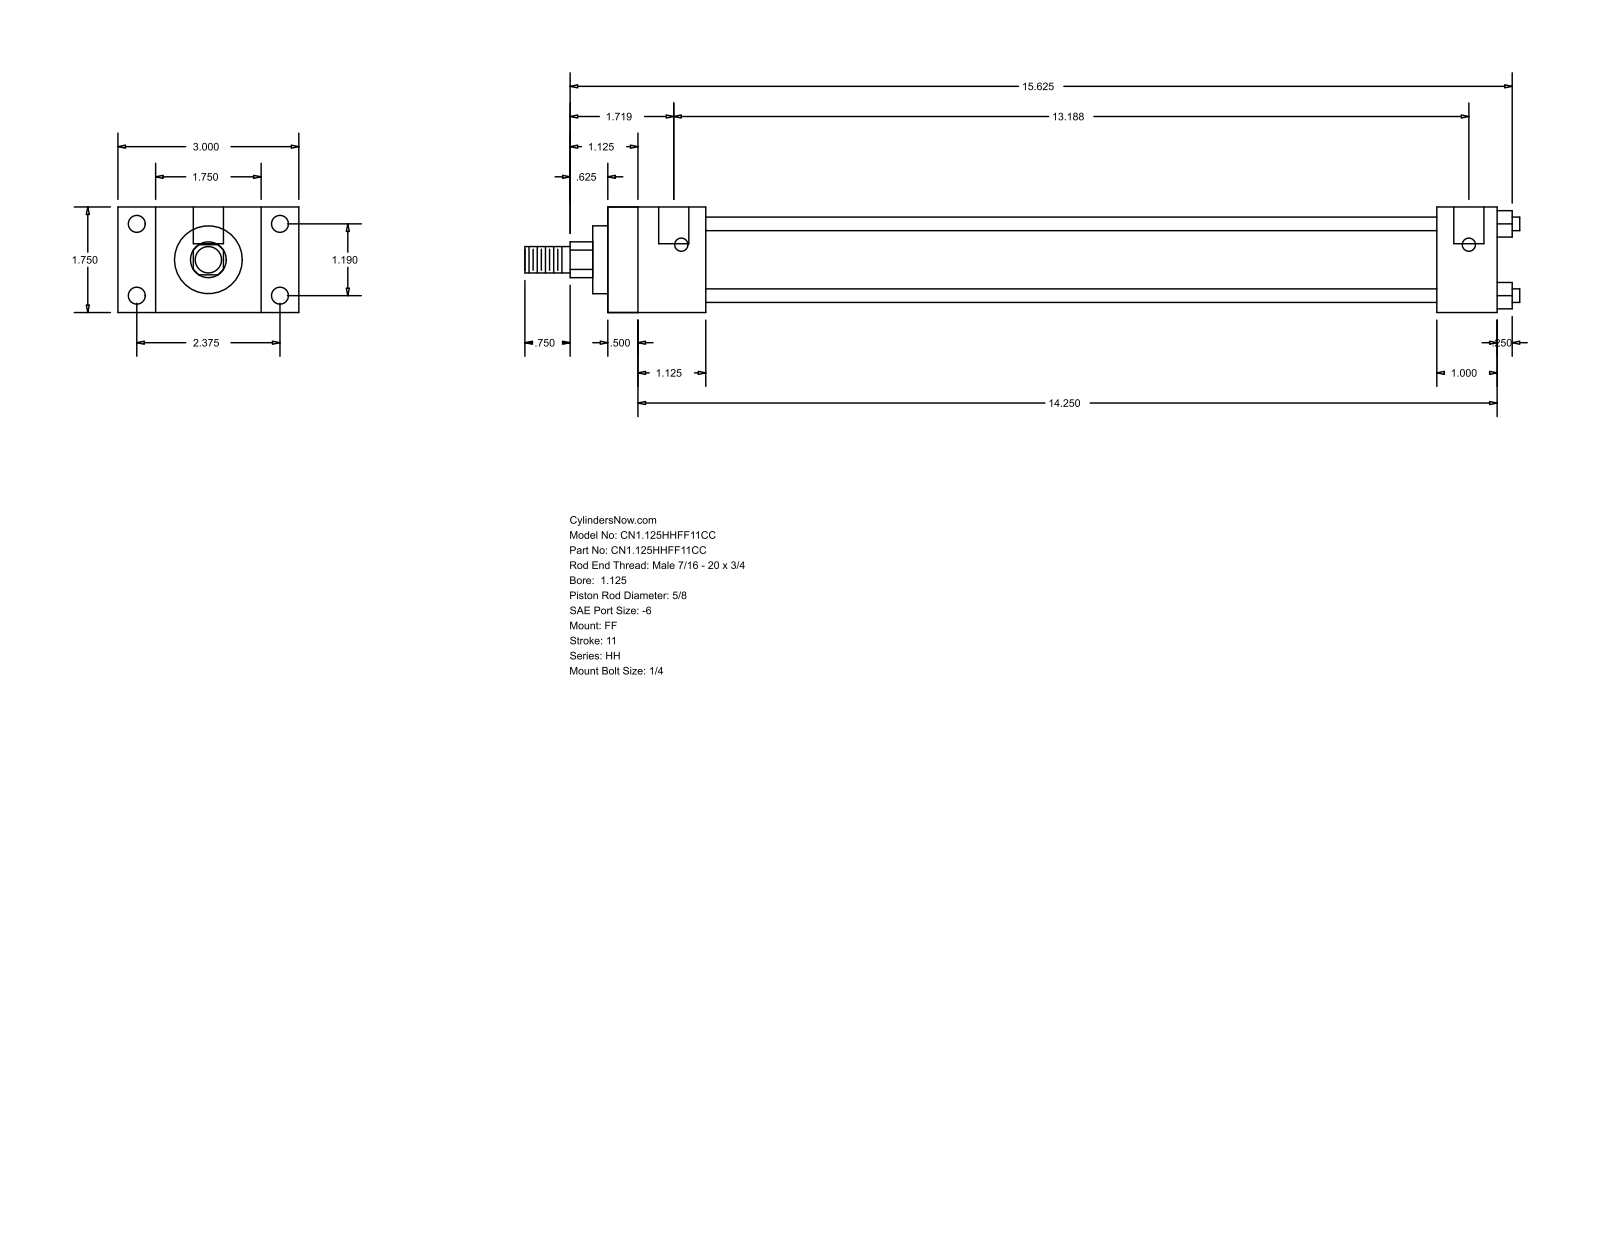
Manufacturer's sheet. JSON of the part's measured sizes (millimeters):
{"part_name": "HH_FF__0112_0.625", "step_written_by": "GSSL Pune (CONFIG_CONTROL_DESIGN)", "units": "millimeters", "bodies": {"solids": 0, "faces": 92, "planar": 64, "cylindrical": 28, "other": 0}, "overall_size": [419.1, 76.2, 44.45], "round_holes": [[5.56, 4], [7.14, 4], [12.7, 2]], "round_bosses_or_shafts": [[5.71, 4], [34.92, 1], [28.57, 1], [15.88, 1], [11.11, 1]], "partial_cylinders_radius": [[7.54, 1]], "face_to_face_distances": [44.46, 374.64, 12.69, 361.95, 15.87, 28.58, 60.33, 25.4, 41.27, 349.24], "hole_center_spacings": [30.22, 60.32, 67.47, 331.79, 3.17, 334.96]}
